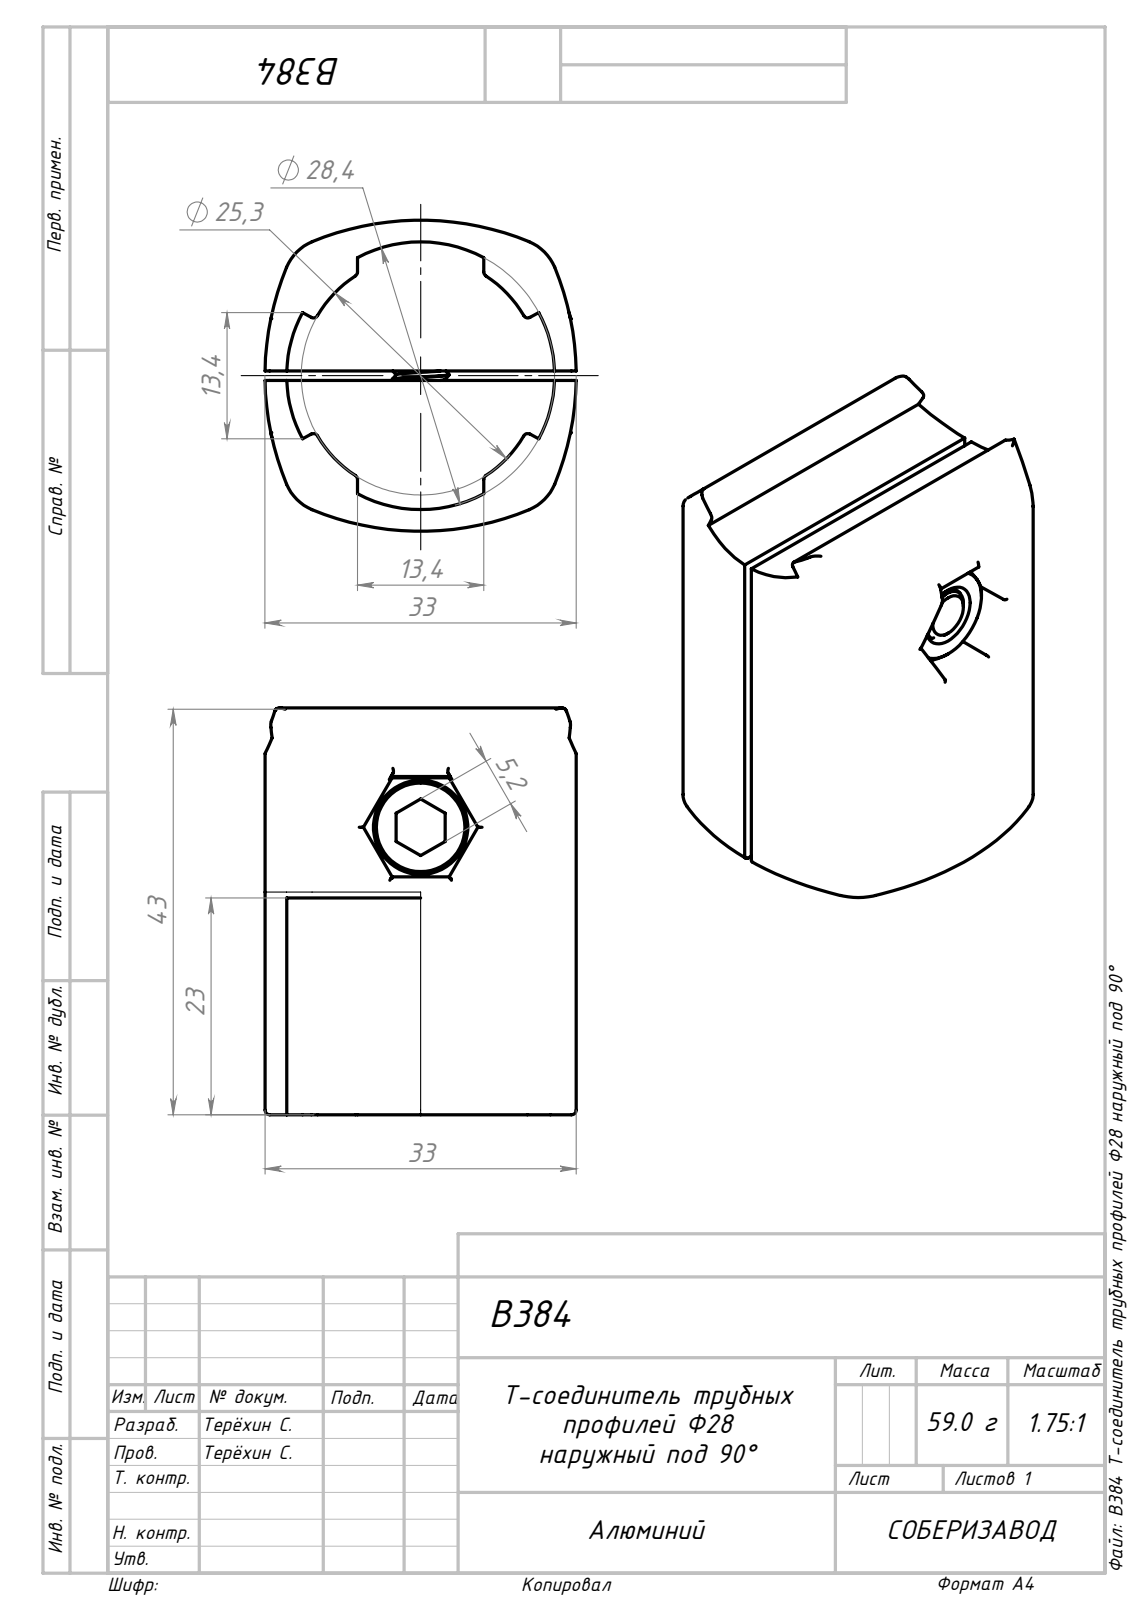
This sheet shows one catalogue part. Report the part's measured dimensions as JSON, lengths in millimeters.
{"part_name": "B384 Т-соединитель трубных профилей Ф28 наружный под 90°", "step_written_by": "SolidWorks 2022 (AUTOMOTIVE_DESIGN)", "units": "millimeters", "bodies": {"solids": 4, "faces": 313, "planar": 98, "cylindrical": 120, "other": 95}, "overall_size": [43.16, 33, 32.99], "volume_mm3": 20798, "surface_area_mm2": 12452, "round_holes": [[5.2, 1], [6.5, 1], [28.4, 1]], "round_bosses_or_shafts": [[10, 1], [6, 1]], "partial_cylinders_radius": [[0.5, 18], [1, 16], [0.2, 4], [5, 4], [30, 4], [12.45, 1], [12.65, 1], [14.2, 1]], "face_to_face_distances": [1, 6, 7, 10.28, 13, 23, 10, 14, 20, 28]}
